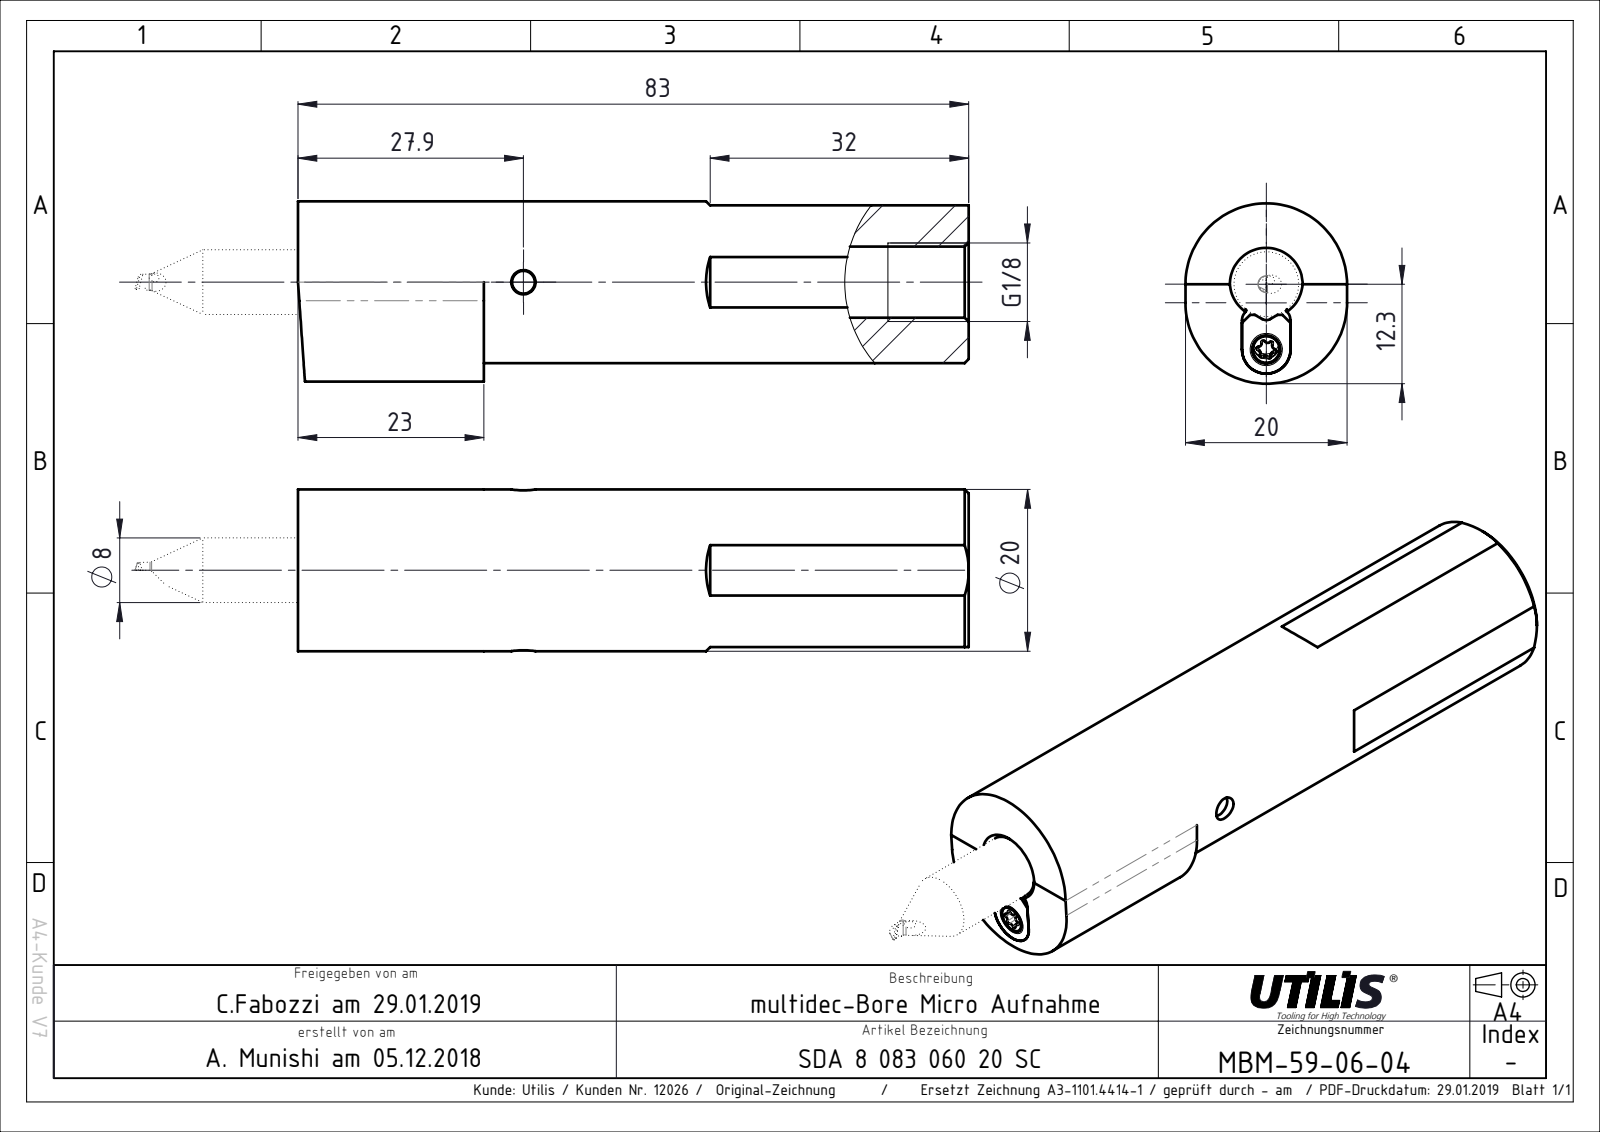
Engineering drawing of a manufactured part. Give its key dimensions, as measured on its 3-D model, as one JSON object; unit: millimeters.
{"part_name": "MBM-59-06-04", "step_written_by": "SolidWorks 2018 (CONFIG_CONTROL_DESIGN)", "units": "millimeters", "bodies": {"solids": 1, "faces": 44, "planar": 13, "cylindrical": 15, "other": 16}, "overall_size": [83, 22.3, 20], "volume_mm3": 21625, "surface_area_mm2": 8407, "round_holes": [[3, 1], [3.3, 1], [8, 1], [8.8, 1]], "round_bosses_or_shafts": [[20, 1]], "partial_cylinders_radius": [[3, 1], [10, 1]], "face_to_face_distances": [83, 7, 13, 0.5, 19.5, 20, 23, 60, 6.5, 6]}
